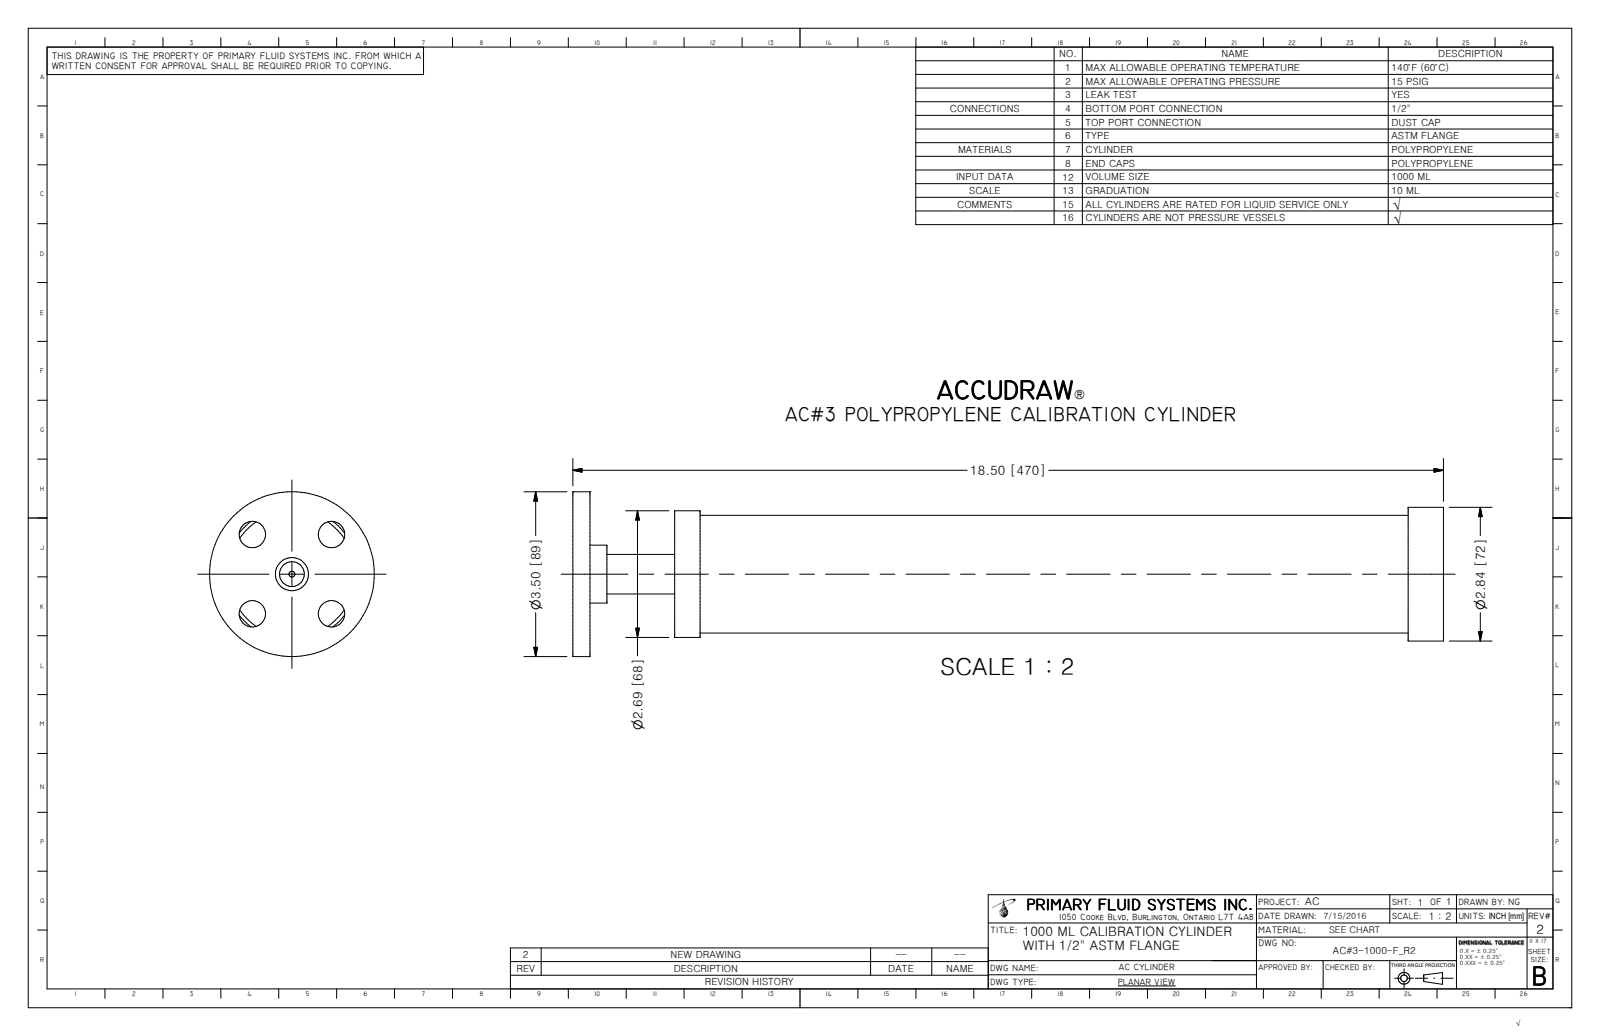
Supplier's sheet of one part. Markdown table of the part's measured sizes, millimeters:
| quantity | value |
| --- | --- |
| part name | AC#3-1000-F_R2; SA-50FLG-PP_R0; FLG-50PP_R0; PIPE-50PP-SCH80 (+3 more) |
| STEP written by | Autodesk Inventor 2009 (AUTOMOTIVE_DESIGN) |
| units | millimeters |
| bodies | 5 solids, 36 faces (16 planar, 18 cylindrical, 2 other) |
| overall size | 469.9 × 88.9 × 88.9 |
| volume | 314 000 mm³ |
| surface area | 205 700 mm² |
| round holes (diameter × count) | 14.2 × 4, 13.4 × 1, 17.5 × 1, 17.9 × 1, 21.3 × 1, 60.5 × 1, 65.7 × 1 |
| round bosses / shafts (diameter × count) | 88.9 × 1, 72.1 × 1, 68.3 × 1, 63.5 × 1, 61 × 1, 57.9 × 1, 31.2 × 1 |
| main face-to-face distances | 19.1, 395.9, 9.3, 469.9, 460.6, 450.9, 441.6, 55, 45.7, 414.9 |
| hole center spacings | 30.2, 42.7, 60.5 |
